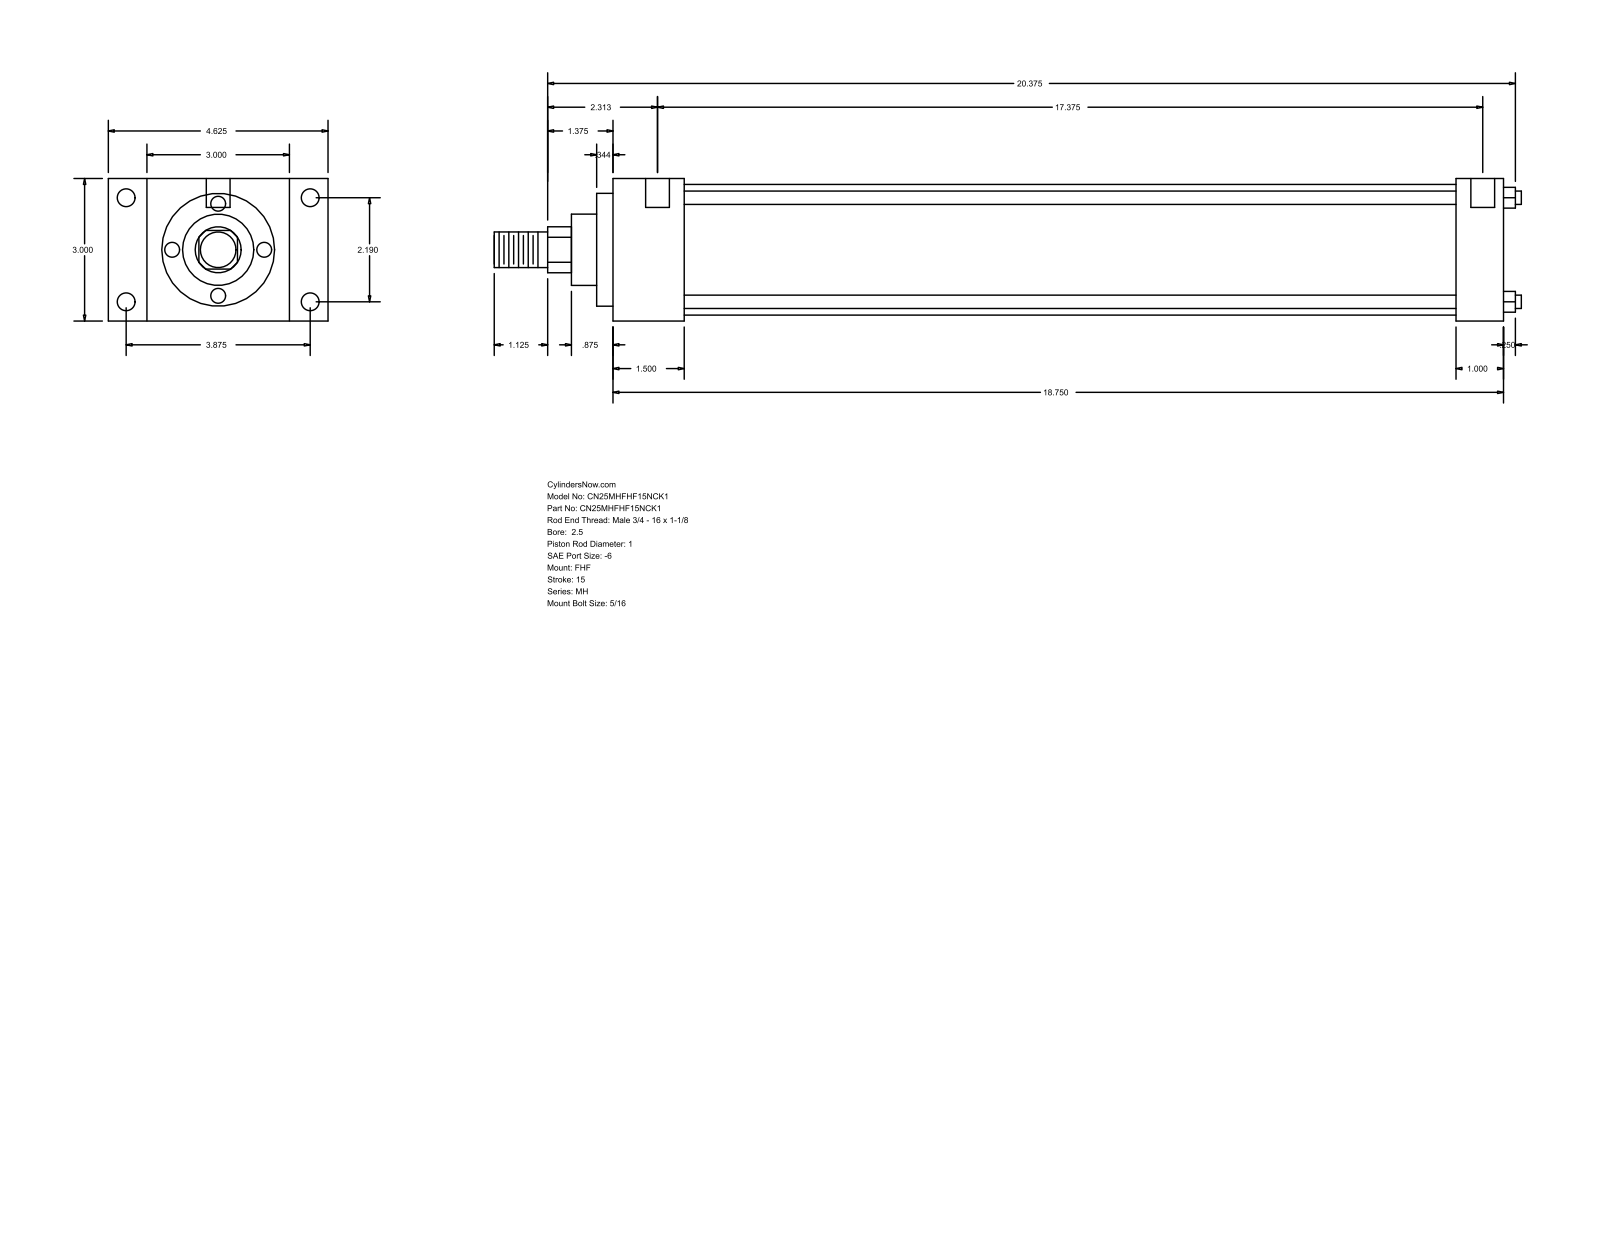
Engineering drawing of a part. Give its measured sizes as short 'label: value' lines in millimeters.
name: MH_FHF__0250_1
written by: GSSL Pune (CONFIG_CONTROL_DESIGN)
unit: mm
bodies: 0 solids, 90 faces (61 planar, 29 cylindrical, 0 other)
size: 549.27 × 117.47 × 76.2
holes: 4× ⌀5.56, 4× ⌀9.53, 2× ⌀12.7
bosses: 4× ⌀7.14, 1× ⌀69.85, 1× ⌀60.33, 1× ⌀38.1, 1× ⌀25.4, 1× ⌀19.05
rounds: 1× R12.29
face distances: 76.2, 476.26, 38.11, 438.15, 20.64, 96.84, 117.48, 450.85, 412.74, 25.41
hole spacings: 55.62, 98.42, 113.05, 449.26, 3.18, 4.76, 441.32, 444.5
